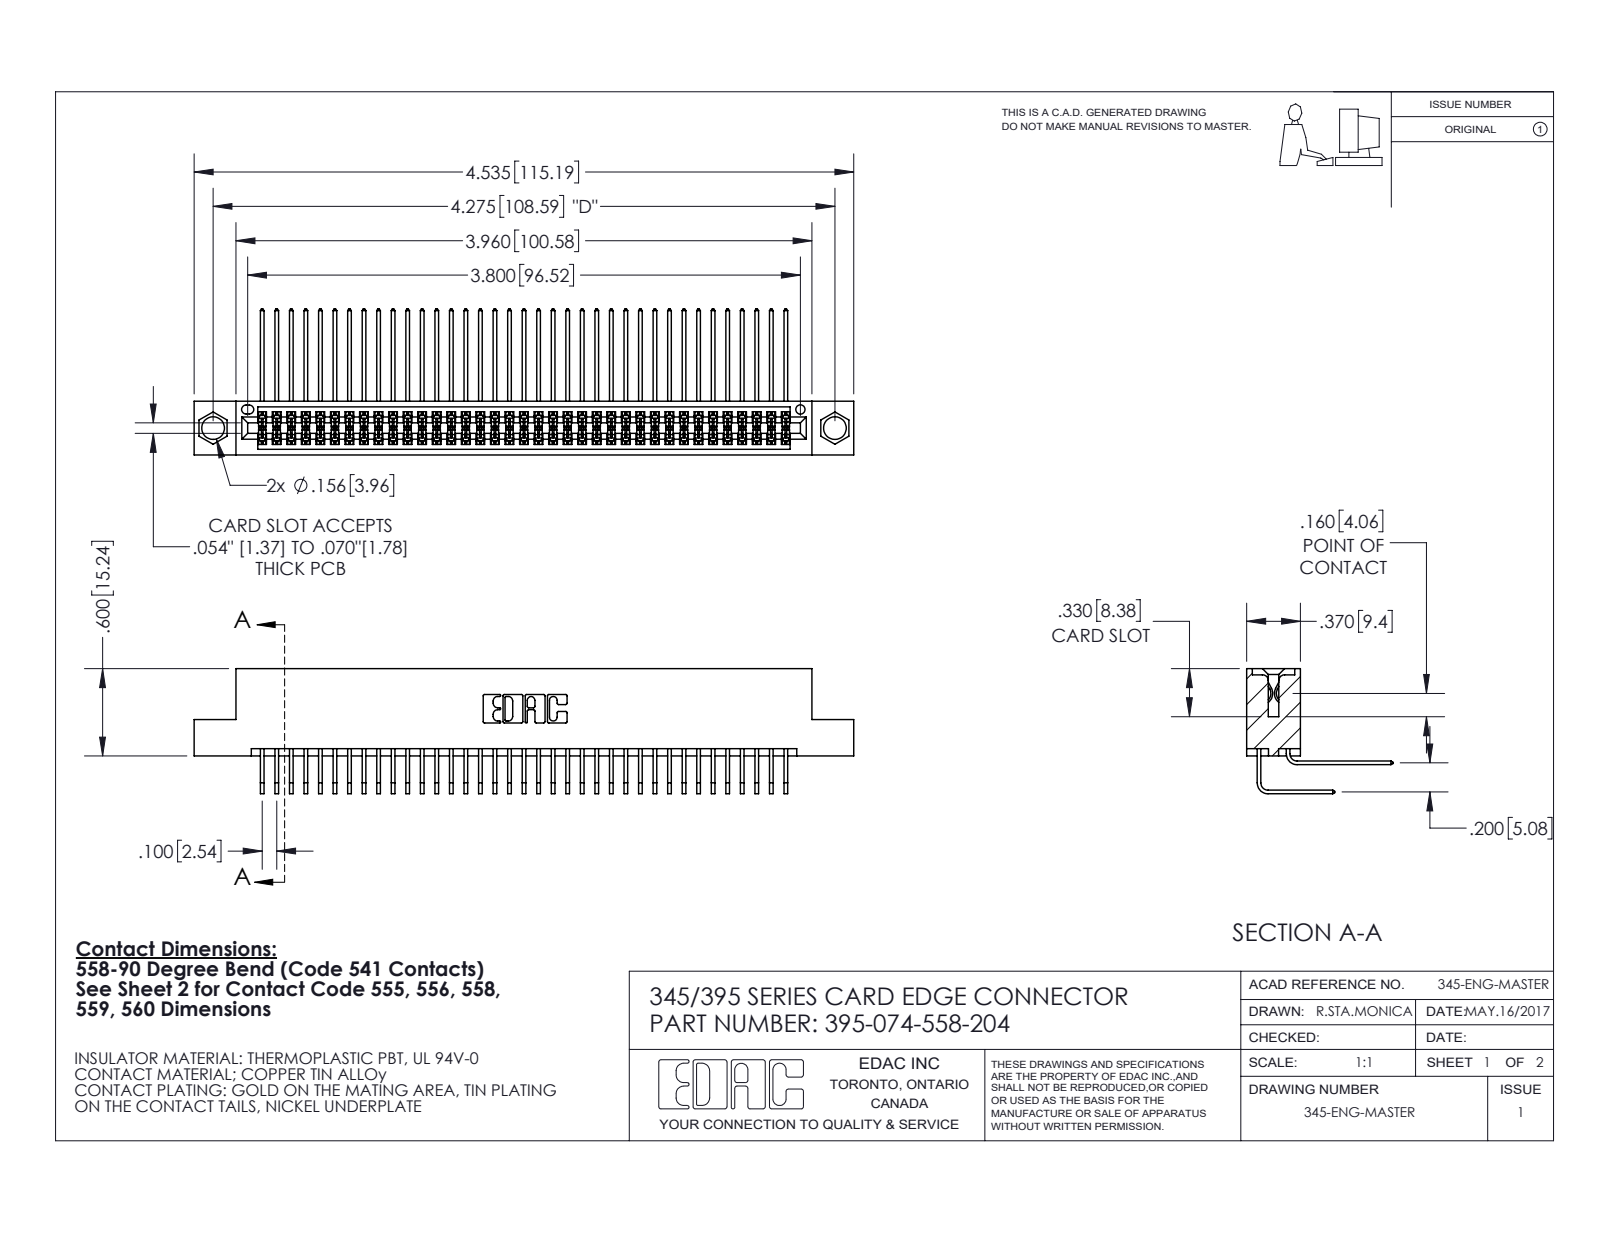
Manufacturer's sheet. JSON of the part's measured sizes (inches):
{"part_name": "345 Part_Flush Mounting Lugs - 0.156 Dia-TI; 345-292-001_558 559 Tail - 1; 395-074-558-204; 345-292-001_558 Tail - 2", "step_written_by": "SolidWorks 2020 (CONFIG_CONTROL_DESIGN)", "units": "inches", "bodies": {"solids": 75, "faces": 3988, "planar": 2684, "cylindrical": 1304, "other": 0}, "overall_size": [4.535, 1.005, 0.859], "volume_in3": 0.7, "surface_area_in2": 29, "round_holes": [[0.156, 2], [0.064, 1]], "partial_cylinders_radius": [[0.006, 111], [0.01, 22], [0.007, 6], [0.031, 6], [0.026, 3], [0.014, 2], [0.019, 2], [0.022, 2]], "face_to_face_distances": [0.072, 0.298, 0.2, 0.37, 0.098, 0.272, 0.025, 0.225, 0.025, 0.175], "hole_center_spacings": [0.27, 4.039, 4.275]}
